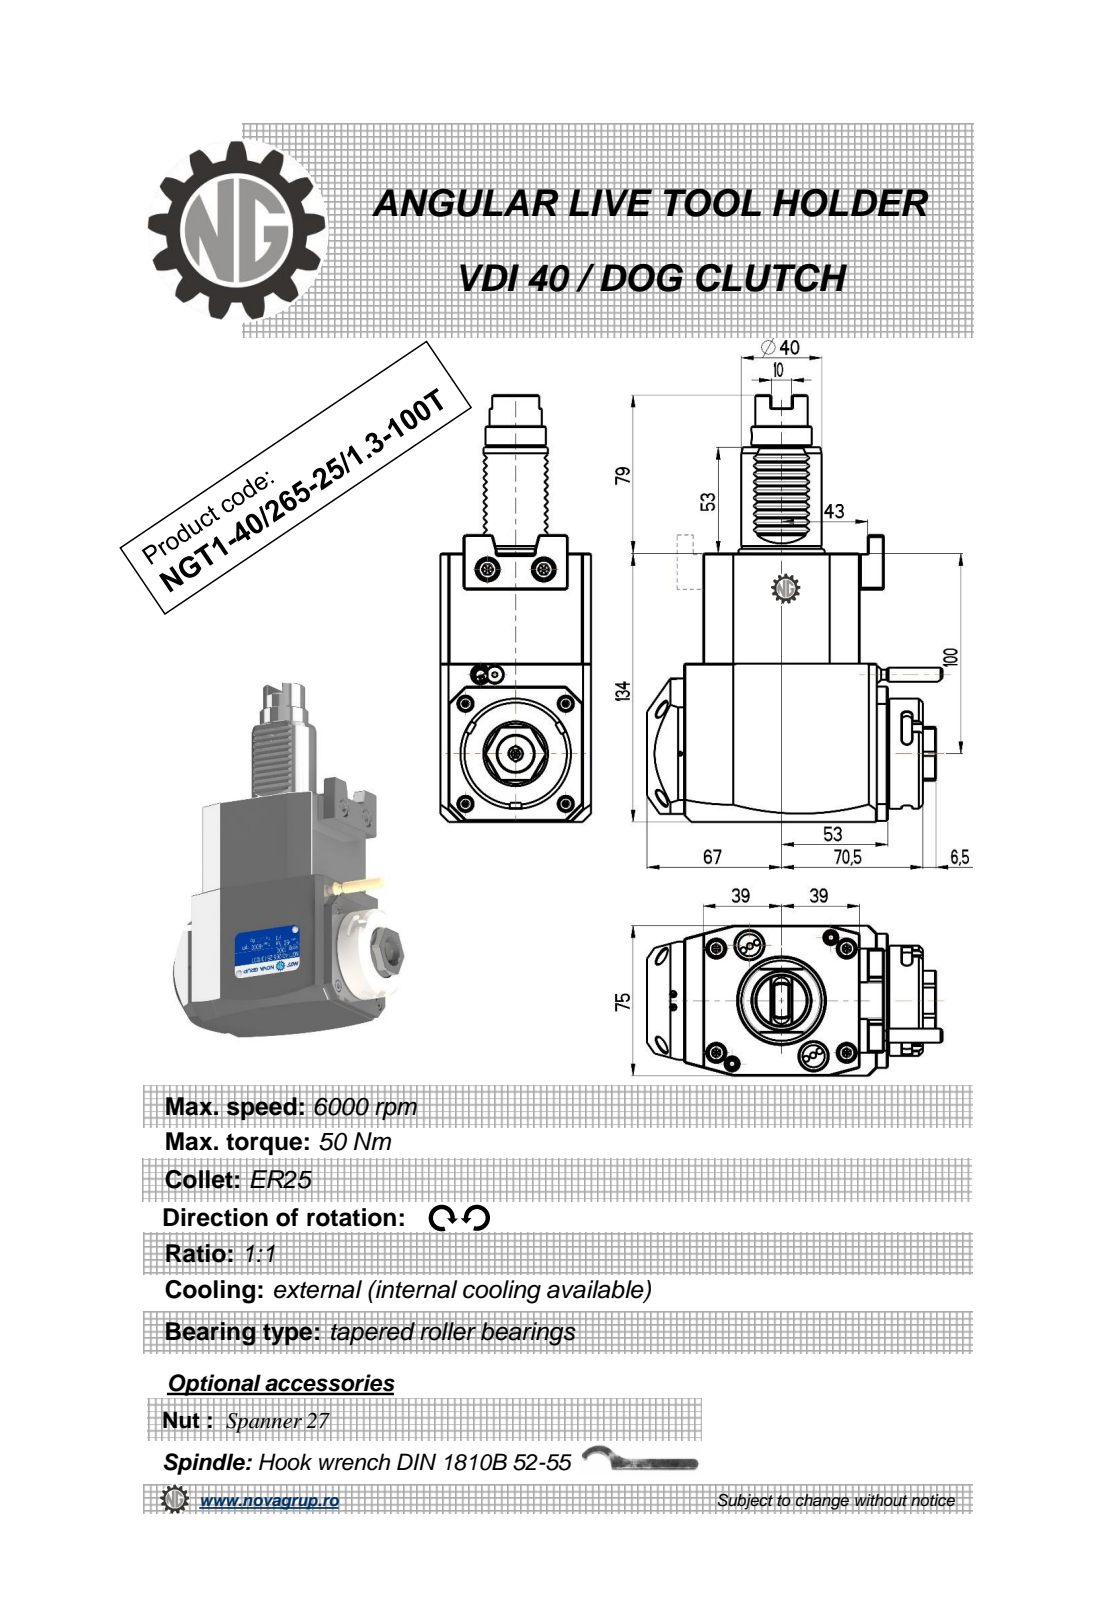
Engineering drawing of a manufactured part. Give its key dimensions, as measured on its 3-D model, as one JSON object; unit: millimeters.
{"part_name": "NGT1_40_265_25_1_3_100T", "step_written_by": "PRO/ENGINEER BY PARAMETRIC TECHNOLOGY CORPORATION, 2010280 (CONFIG_CONTROL_DESIGN)", "units": "millimeters", "bodies": {"solids": 1, "faces": 383, "planar": 239, "cylindrical": 78, "other": 66}, "overall_size": [213, 147.33, 75], "volume_mm3": 1073000, "surface_area_mm2": 77259, "round_holes": [[2.5, 1], [3, 1], [4.2, 1], [18, 1]], "round_bosses_or_shafts": [[55, 1], [48, 1], [40, 1], [30, 1], [26, 1], [8, 1], [7, 1], [5, 1]], "partial_cylinders_radius": [[0.3, 20], [0.26, 6], [2.5, 6], [0.5, 2], [1, 2], [180, 2], [12.5, 1], [15, 1]], "face_to_face_distances": [75, 134, 78, 14, 92, 17.5, 31.5, 84.88, 109.5, 4], "hole_center_spacings": [43.2, 120.28, 158.5]}
